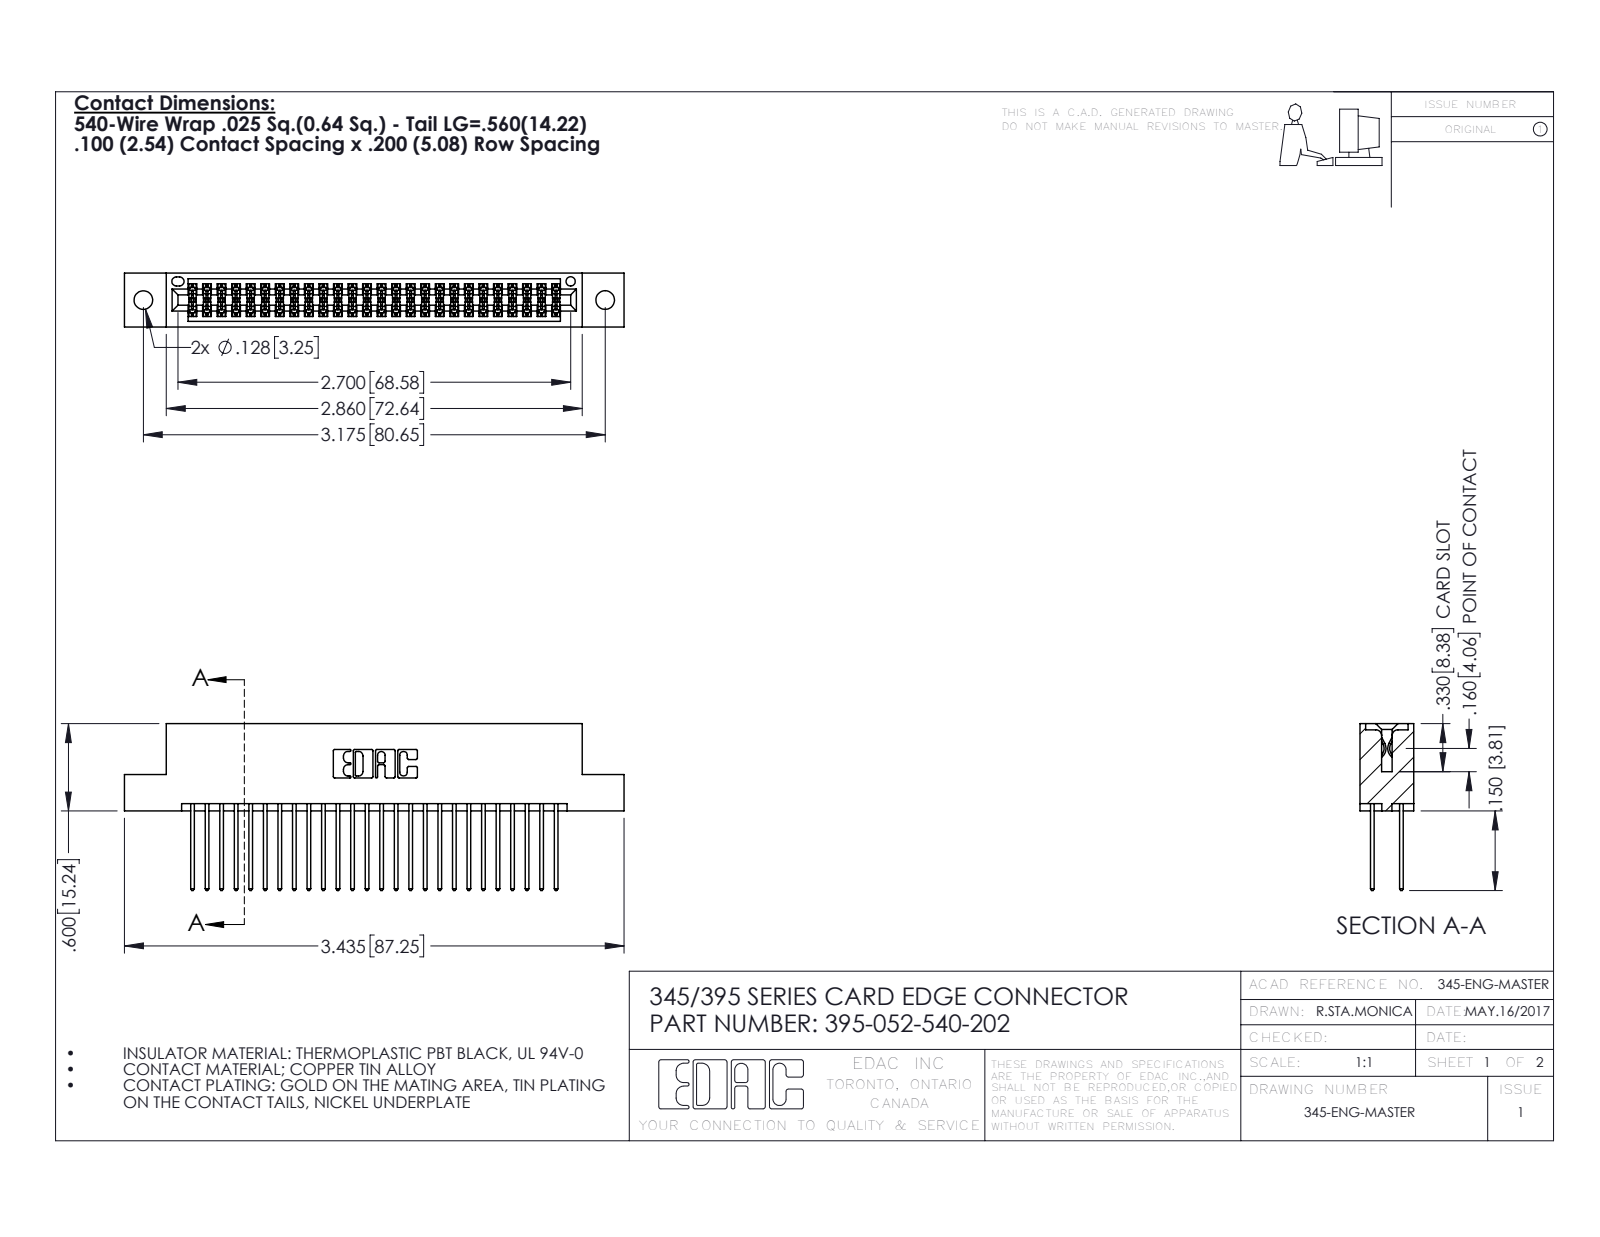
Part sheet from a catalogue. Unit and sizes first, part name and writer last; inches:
Units: inches
Overall size (bounding box): 3.435 × 1.147 × 0.37
Round holes (diameter × count): ⌀0.128 ×2, ⌀0.064 ×1
Partial cylindrical surfaces — rounded edges, fillets, slot ends (radius × count): R0.006 ×78, R0.01 ×52, R0.01 ×22, R0.007 ×6, R0.031 ×6, R0.026 ×3, R0.014 ×2, R0.019 ×2
Main face-to-face distances: 0.298, 0.072, 0.2, 0.098, 0.272, 0.025, 0.37, 0.225, 0.175, 0.149
Hole centre spacings: 0.27, 2.94, 3.175
Volume: 0.518 in³ · Surface area: 19.96 in²
Bodies: 53 solids, 2726 faces (1796 planar, 930 cylindrical, 0 other)
Part name (STEP PRODUCT): 395-052-540-202; 345 Part_Flush Mounting Lugs - 0.128 Dia; 345-292-001_345-293-140
STEP written by: SolidWorks 2016 (CONFIG_CONTROL_DESIGN)
